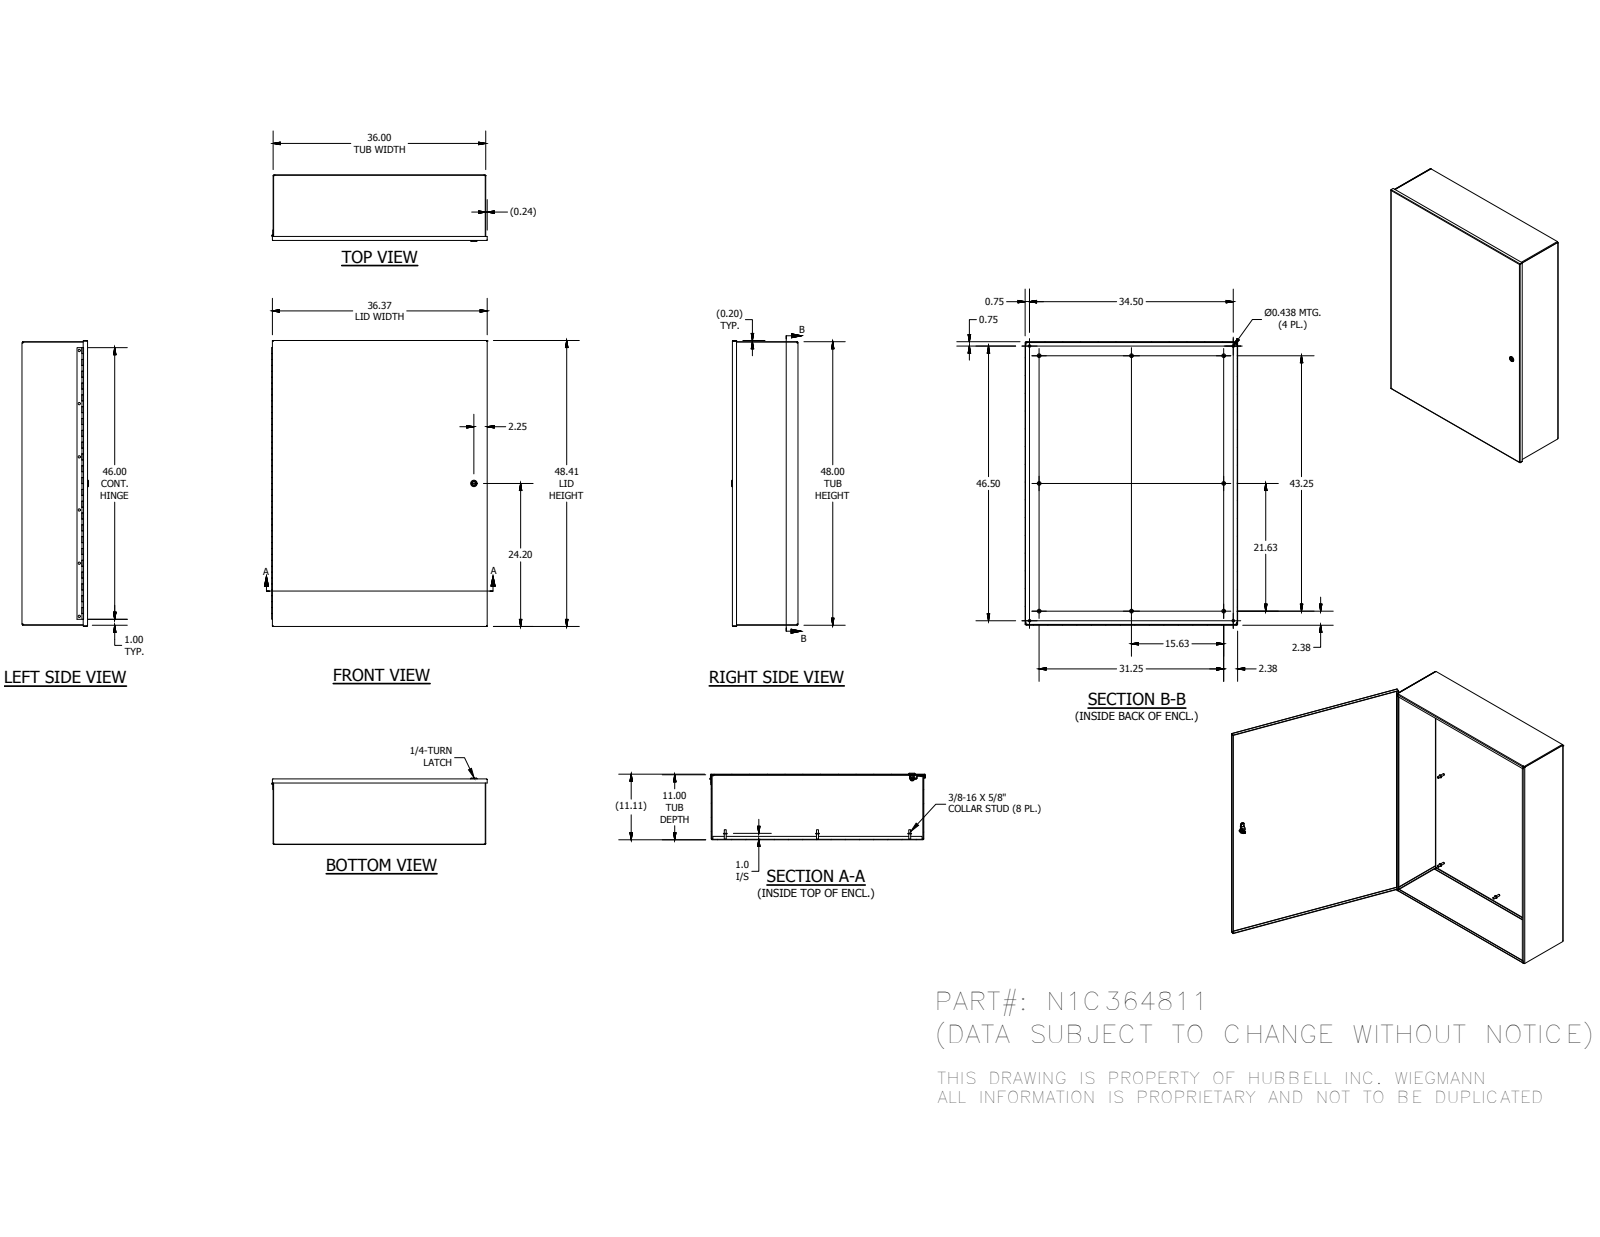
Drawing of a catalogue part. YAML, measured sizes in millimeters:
part_name: "N1C364811BLR; N1C3611TB; N1C3648LID; 1000-101-GPF_GPD (+8 more)"
step_written_by: "Autodesk Inventor 2016 (AUTOMOTIVE_DESIGN)"
units: millimeters
bodies: {solids: 22, faces: 1042, planar: 681, cylindrical: 291, other: 70}
overall_size: [1229.52, 926.81, 286.07]
volume: 6838000
surface_area: 7321000
round_holes:
  - {diameter: 9.52, count: 6}
  - {diameter: 11.11, count: 4}
  - {diameter: 3.17, count: 1}
  - {diameter: 5, count: 1}
  - {diameter: 8, count: 1}
  - {diameter: 10, count: 1}
  - {diameter: 10.2, count: 1}
  - {diameter: 16.1, count: 1}
  - {diameter: 20.38, count: 1}
round_bosses_or_shafts:
  - {diameter: 15.88, count: 8}
  - {diameter: 8.38, count: 8}
  - {diameter: 28, count: 1}
  - {diameter: 27, count: 1}
  - {diameter: 23, count: 1}
  - {diameter: 19.8, count: 1}
  - {diameter: 15.8, count: 1}
  - {diameter: 15.2, count: 1}
partial_cylinders:
  - {radius: 0.3, count: 30}
  - {radius: 3.47, count: 12}
  - {radius: 1.59, count: 11}
  - {radius: 0.5, count: 10}
  - {radius: 0.79, count: 4}
  - {radius: 2.67, count: 4}
  - {radius: 4, count: 4}
  - {radius: 0.4, count: 3}
face_to_face_distances: [1.88, 280.19, 278.31, 282.07, 912.52, 1217.32, 910.64, 914.4, 1215.44, 1219.2]
hole_center_spacings: [228.6, 457.2, 685.8, 591.42, 876.3, 914.4, 1030.3, 1181.1]
